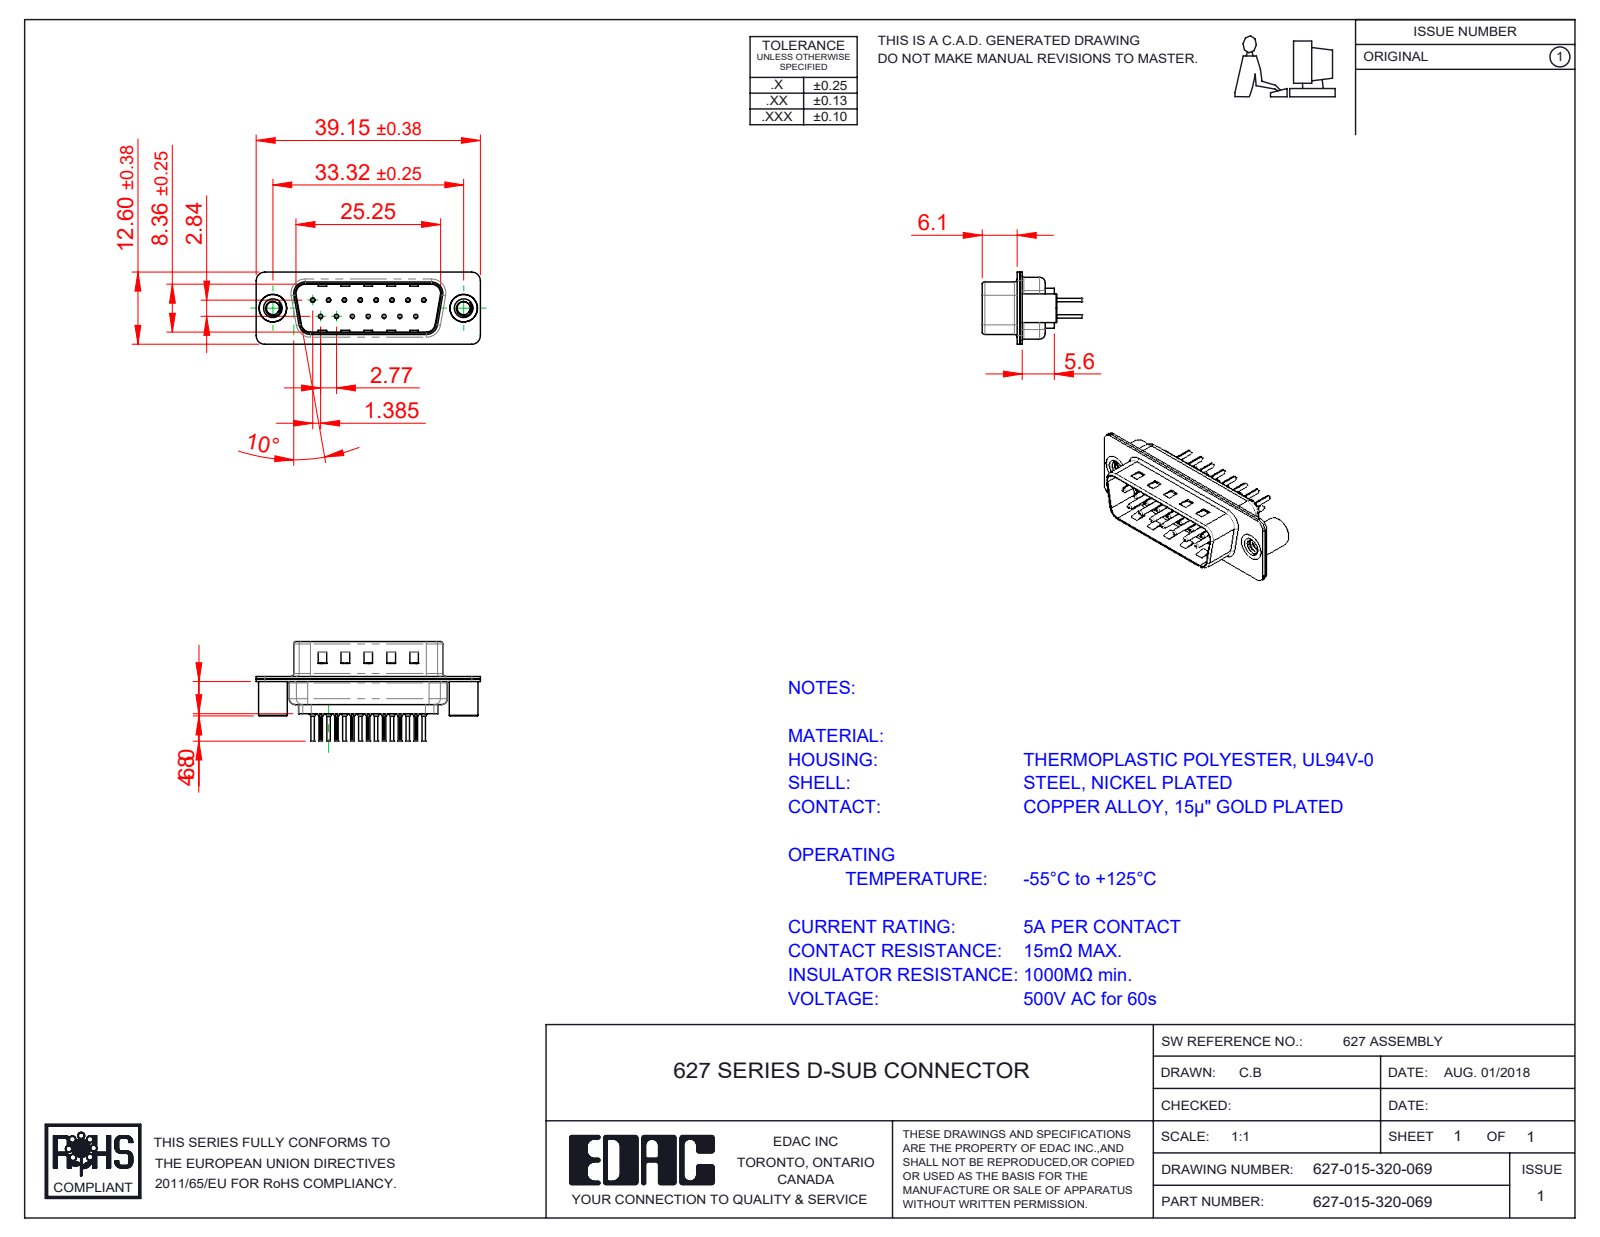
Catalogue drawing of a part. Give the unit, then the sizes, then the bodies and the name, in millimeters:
Units: millimetres
Overall size (bounding box): 39.15 × 17.3 × 12.6
Round holes (diameter × count): ⌀0.2 ×15, ⌀0.35 ×15, ⌀1.1 ×15, ⌀1.6 ×15, ⌀2.26 ×2, ⌀4 ×2, ⌀4.8 ×2
Round bosses / shafts (diameter × count): ⌀2 ×15, ⌀1.5 ×15, ⌀0.75 ×15, ⌀0.6 ×15, ⌀5 ×2, ⌀4.9 ×2
Partial cylindrical surfaces — rounded edges, fillets, slot ends (radius × count): R0.1 ×30, R1.5 ×16, R2 ×12, R0.5 ×8, R1.6 ×8, R0.25 ×4, R0.6 ×4, R0.65 ×4
Main face-to-face distances: 0.4, 0.45, 0.9, 0.82, 9.58, 8.76, 1.5, 1.4, 6.5, 5.6
Hole centre spacings: 3.16, 2.77, 5.54, 8.31, 11.08, 5.03, 5.04, 7.48
Volume: 1 927 mm³ · Surface area: 5 583 mm²
Bodies: 20 solids, 1832 faces (499 planar, 708 cylindrical, 625 other)
Part name (STEP PRODUCT): 627 4-40 Threaded Standoff BS; 627 Shell Rear_15 Contacts; 627 Contact Row 1_20L; 627-015-320-069 (+3 more)
STEP written by: SolidWorks 2020 (CONFIG_CONTROL_DESIGN)
